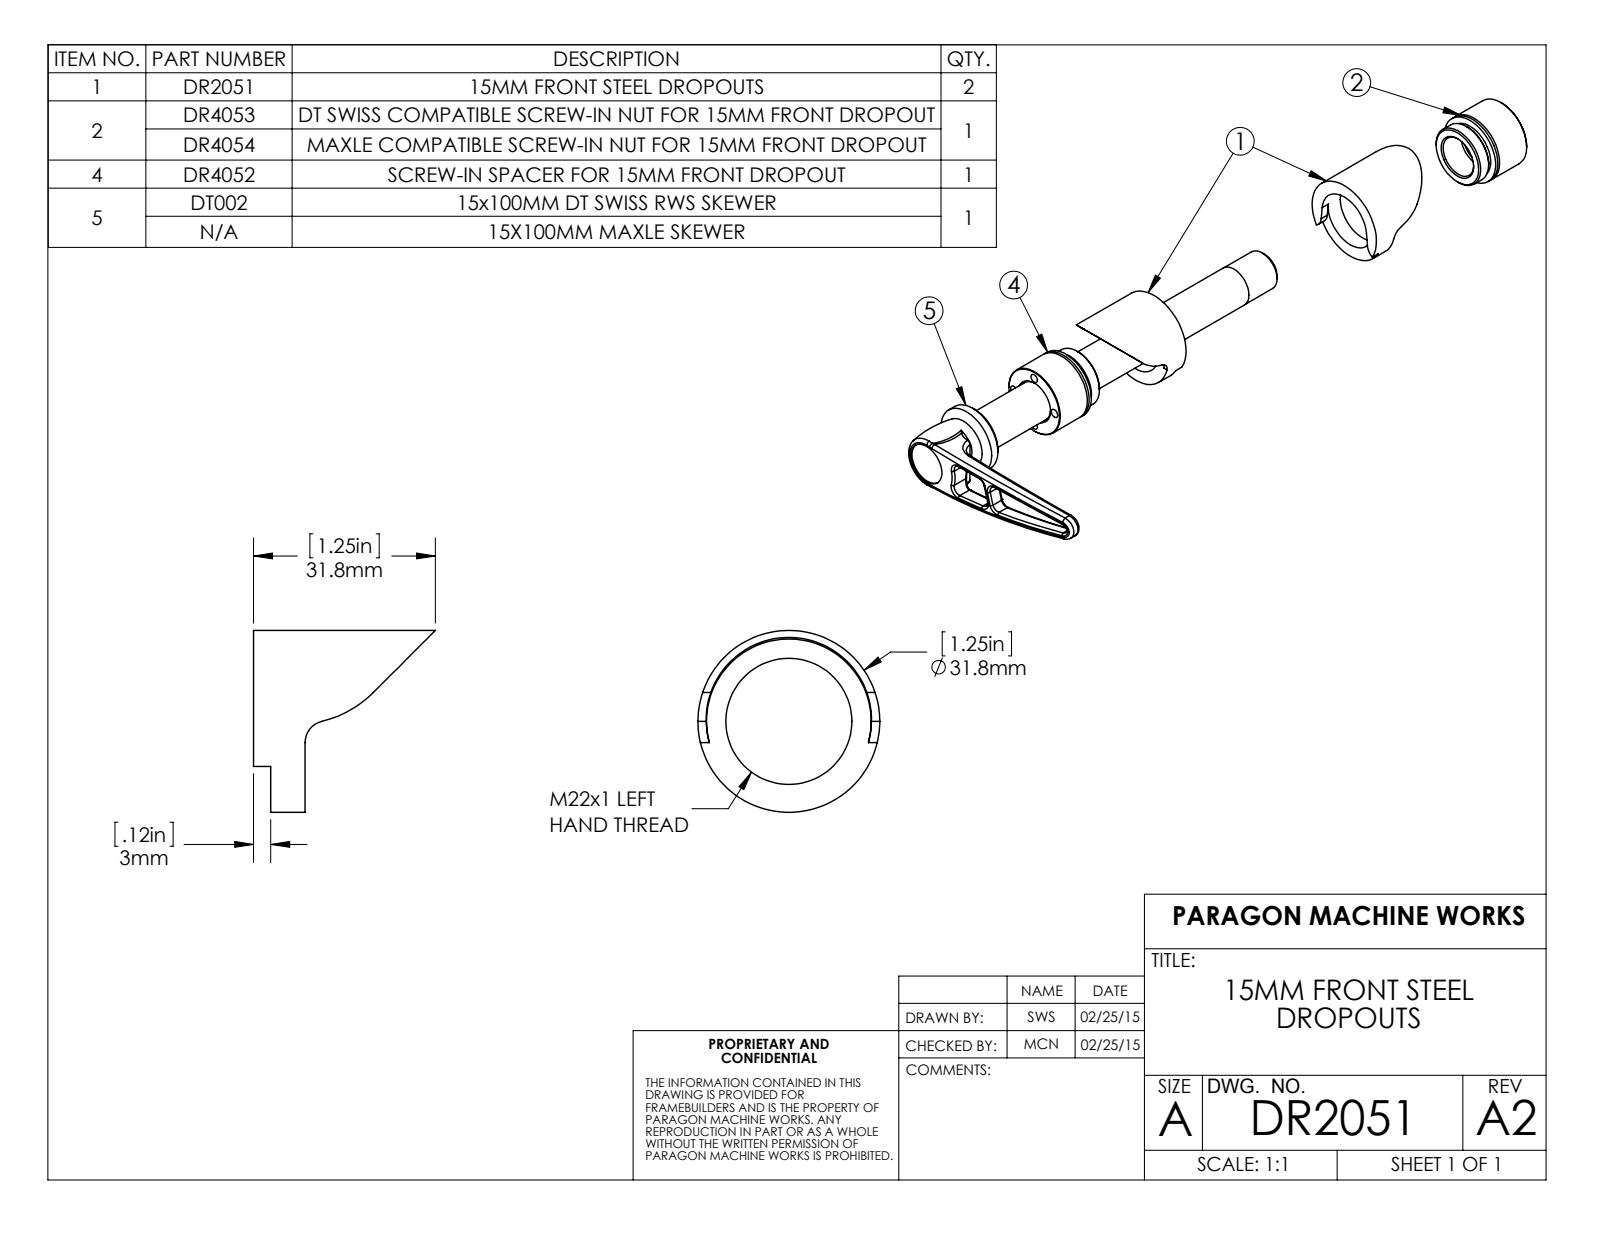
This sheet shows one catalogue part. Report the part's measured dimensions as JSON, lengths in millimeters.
{"part_name": "DR2051; DR4052; DR4053; DT002", "step_written_by": "SolidWorks 2015 (AUTOMOTIVE_DESIGN)", "units": "millimeters", "bodies": {"solids": 5, "faces": 230, "planar": 37, "cylindrical": 92, "other": 101}, "overall_size": [174.13, 80.9, 31.75], "volume_mm3": 56701, "surface_area_mm2": 25604, "round_holes": [[3.17, 4], [3.18, 4], [13.5, 1], [15.06, 1], [15.24, 1], [22, 1]], "round_bosses_or_shafts": [[31.75, 1], [26, 1], [25.4, 1], [24.94, 1], [20.5, 1], [14.91, 1], [14.76, 1]], "partial_cylinders_radius": [[2.54, 6], [2.5, 2], [3.81, 2], [19.05, 2], [505.46, 2], [508, 2], [1.91, 1], [4.45, 1]], "face_to_face_distances": [15.5, 127.5, 24.5, 118.5, 9, 103, 112, 143, 21.7, 121.3], "hole_center_spacings": [10, 14.14, 5.69, 9.54, 17.58, 19.17, 19.99, 20]}
